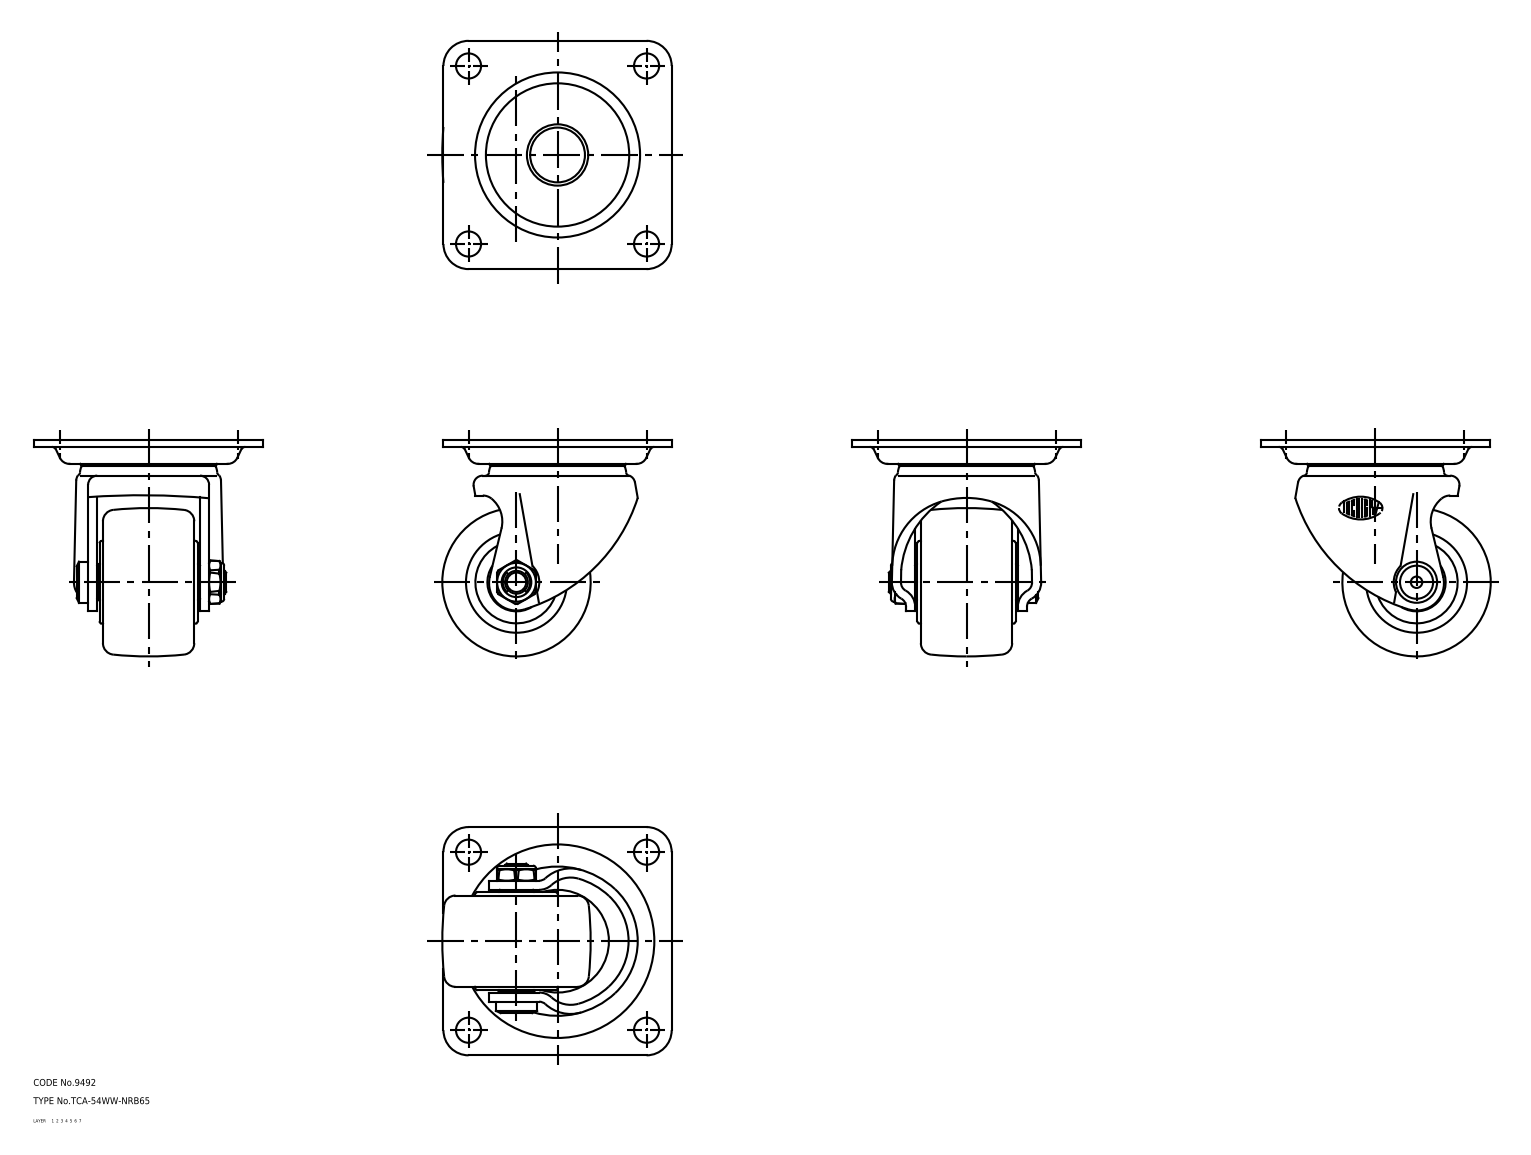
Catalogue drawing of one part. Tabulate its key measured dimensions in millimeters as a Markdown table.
| quantity | value |
| --- | --- |
| part name | seal; nut; main shaft; wheel (+3 more) |
| STEP written by | CADfix (AUTOMOTIVE_DESIGN) |
| units | millimeters |
| bodies | 7 solids, 233 faces (0 planar, 0 cylindrical, 233 other) |
| overall size | 100.5 × 100 × 95 |
| volume | 242 293 mm³ |
| surface area | 72 570 mm² |
